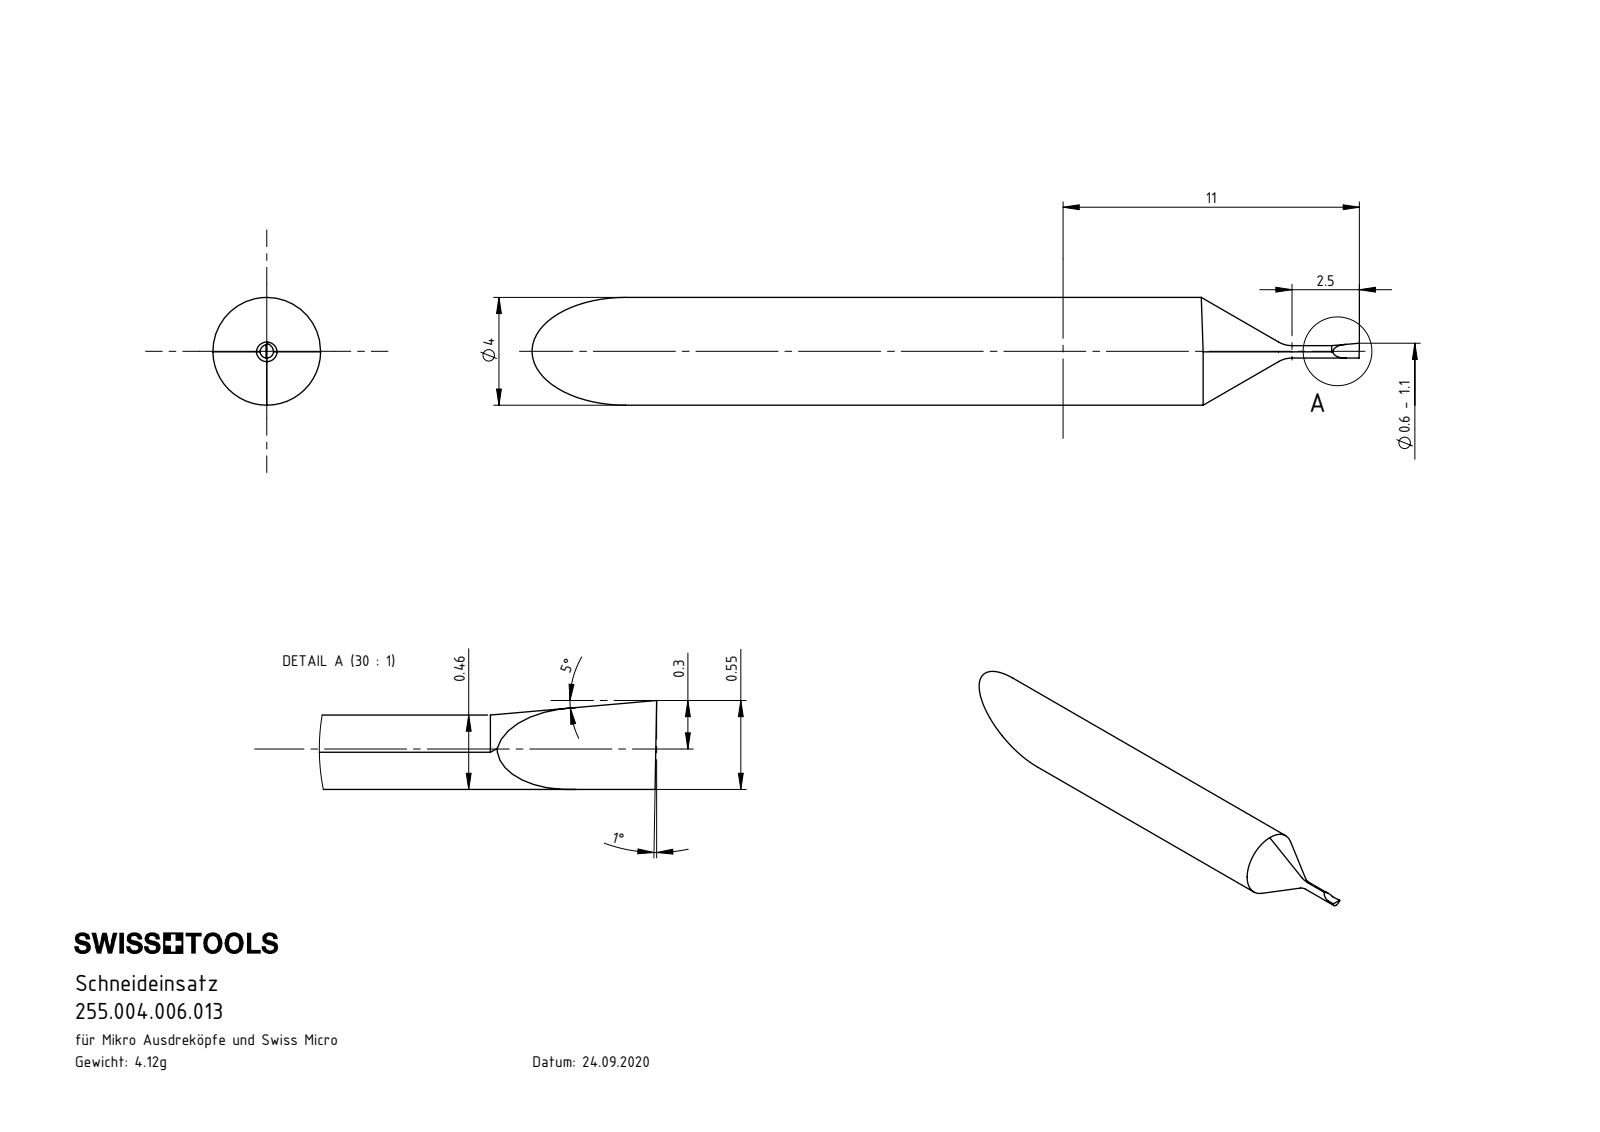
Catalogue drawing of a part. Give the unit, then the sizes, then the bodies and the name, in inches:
Units: inches
Overall size (bounding box): 1.209 × 0.157 × 0.157
Round bosses / shafts (diameter × count): ⌀0.157 ×1
Partial cylindrical surfaces — rounded edges, fillets, slot ends (radius × count): R0.01 ×2, R0.008 ×1, R0.01 ×1, R0.012 ×1
Main face-to-face distances: 0.526
Volume: 0.017 in³ · Surface area: 0.501 in²
Bodies: 1 solid, 26 faces (4 planar, 9 cylindrical, 13 other)
Part name (STEP PRODUCT): A04.0025.02.06.00_YR
STEP written by: SolidWorks 2017 (AUTOMOTIVE_DESIGN)
